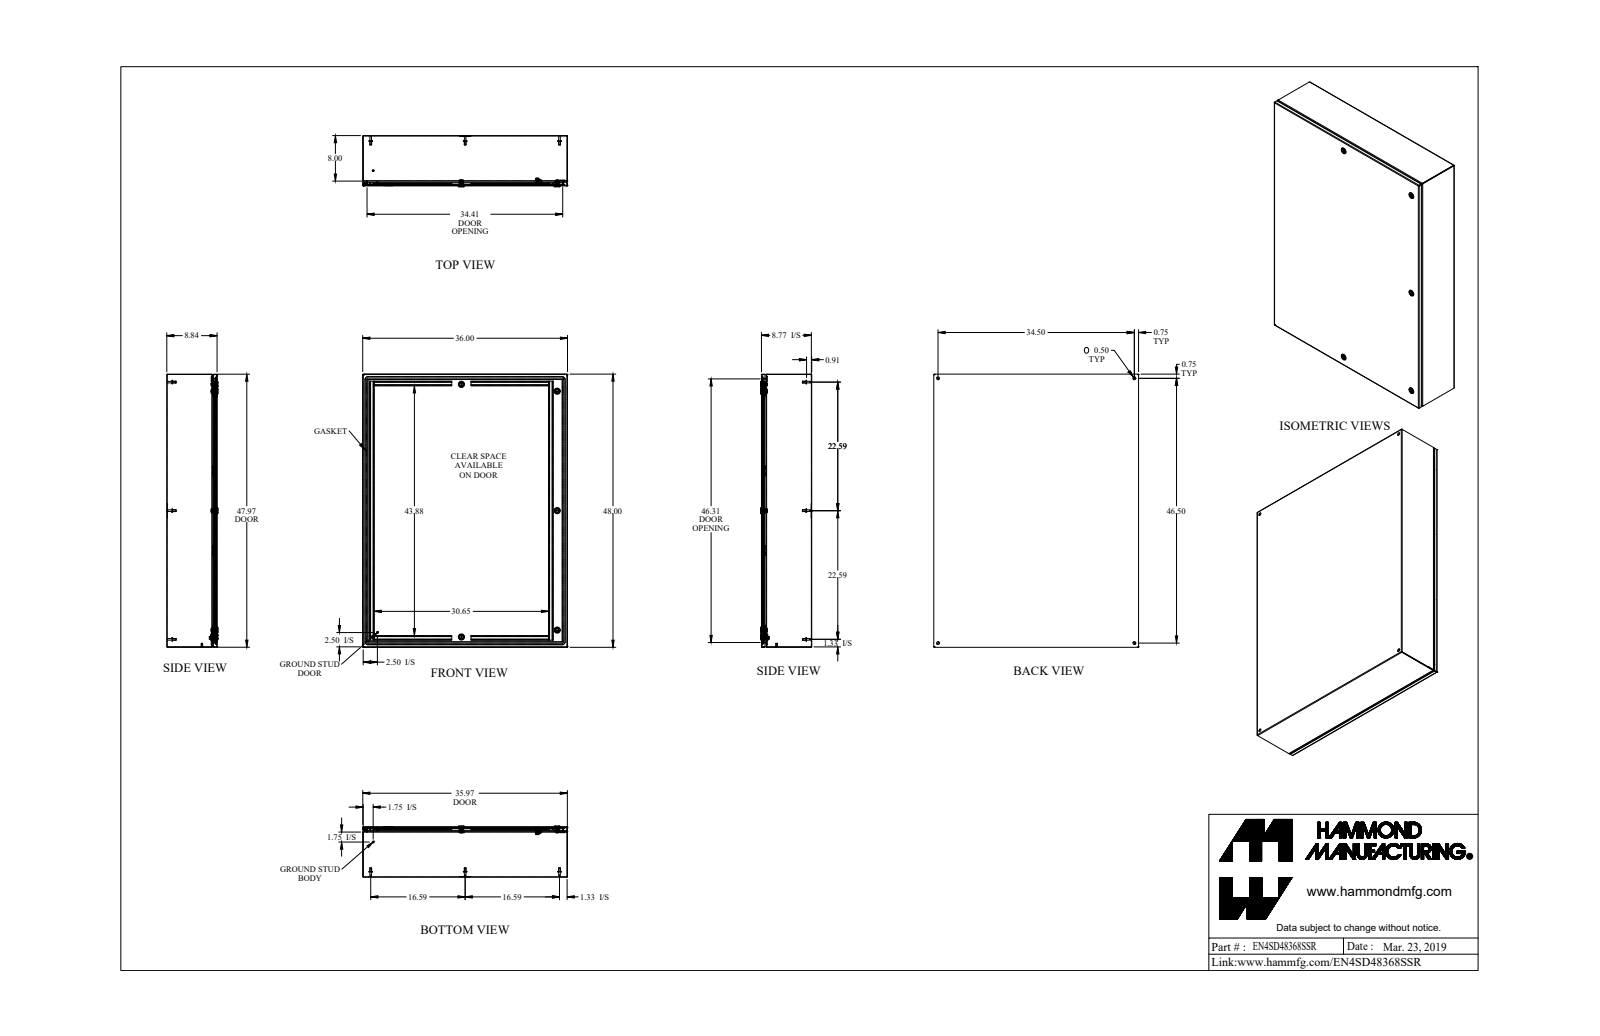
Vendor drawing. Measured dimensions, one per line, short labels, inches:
name: EN4SD48368SSR_Default
written by: SolidWorks 2019 (CONFIG_CONTROL_DESIGN)
unit: in
bodies: 64 solids, 1731 faces (896 planar, 550 cylindrical, 285 other)
size: 48 × 36 × 9.002
volume: 400.5 in³; area: 11 294 in²
holes: 9× ⌀0.5, 5× ⌀0.197, 5× ⌀0.387, 5× ⌀0.63, 5× ⌀0.768, 1× ⌀0.172, 1× ⌀0.196, 1× ⌀0.24, 1× ⌀0.242, 1× ⌀0.275, 1× ⌀0.375
bosses: 11× ⌀0.625, 10× ⌀0.313, 8× ⌀0.275, 5× ⌀1.1, 5× ⌀0.236, 3× ⌀0.785, 3× ⌀0.625, 3× ⌀0.525
rounds: 24× R0.01, 24× R0.048, 21× R0.062, 20× R0.036, 20× R0.108, 10× R0.094, 10× R0.125, 9× R0.016
face distances: 0.072, 8.77, 8.698, 8.842, 35.928, 47.928, 35.856, 36, 47.856, 48
hole spacings: 2.507, 16.622, 16.881, 17.943, 20.985, 23.275, 27.854, 33.504
